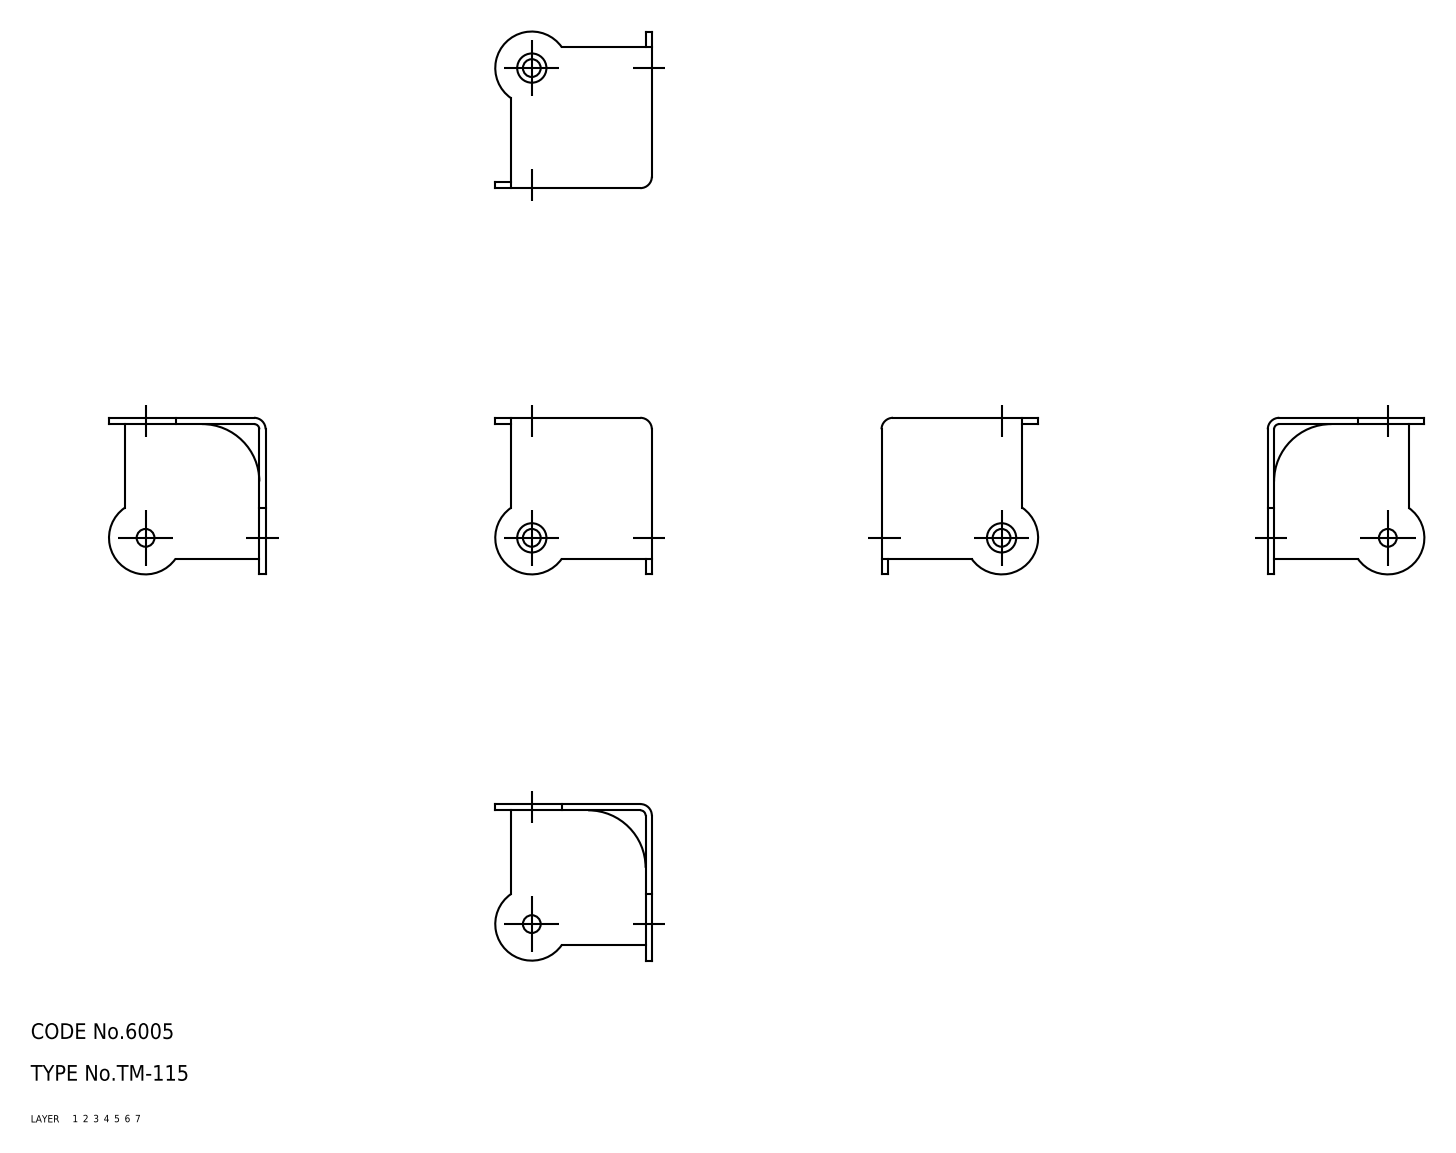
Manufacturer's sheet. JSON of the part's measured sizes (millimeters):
{"part_name": "angle", "step_written_by": "CADfix (AUTOMOTIVE_DESIGN)", "units": "millimeters", "bodies": {"solids": 1, "faces": 32, "planar": 0, "cylindrical": 0, "other": 32}, "overall_size": [30, 30, 30], "volume_mm3": 2211, "surface_area_mm2": 3973}
